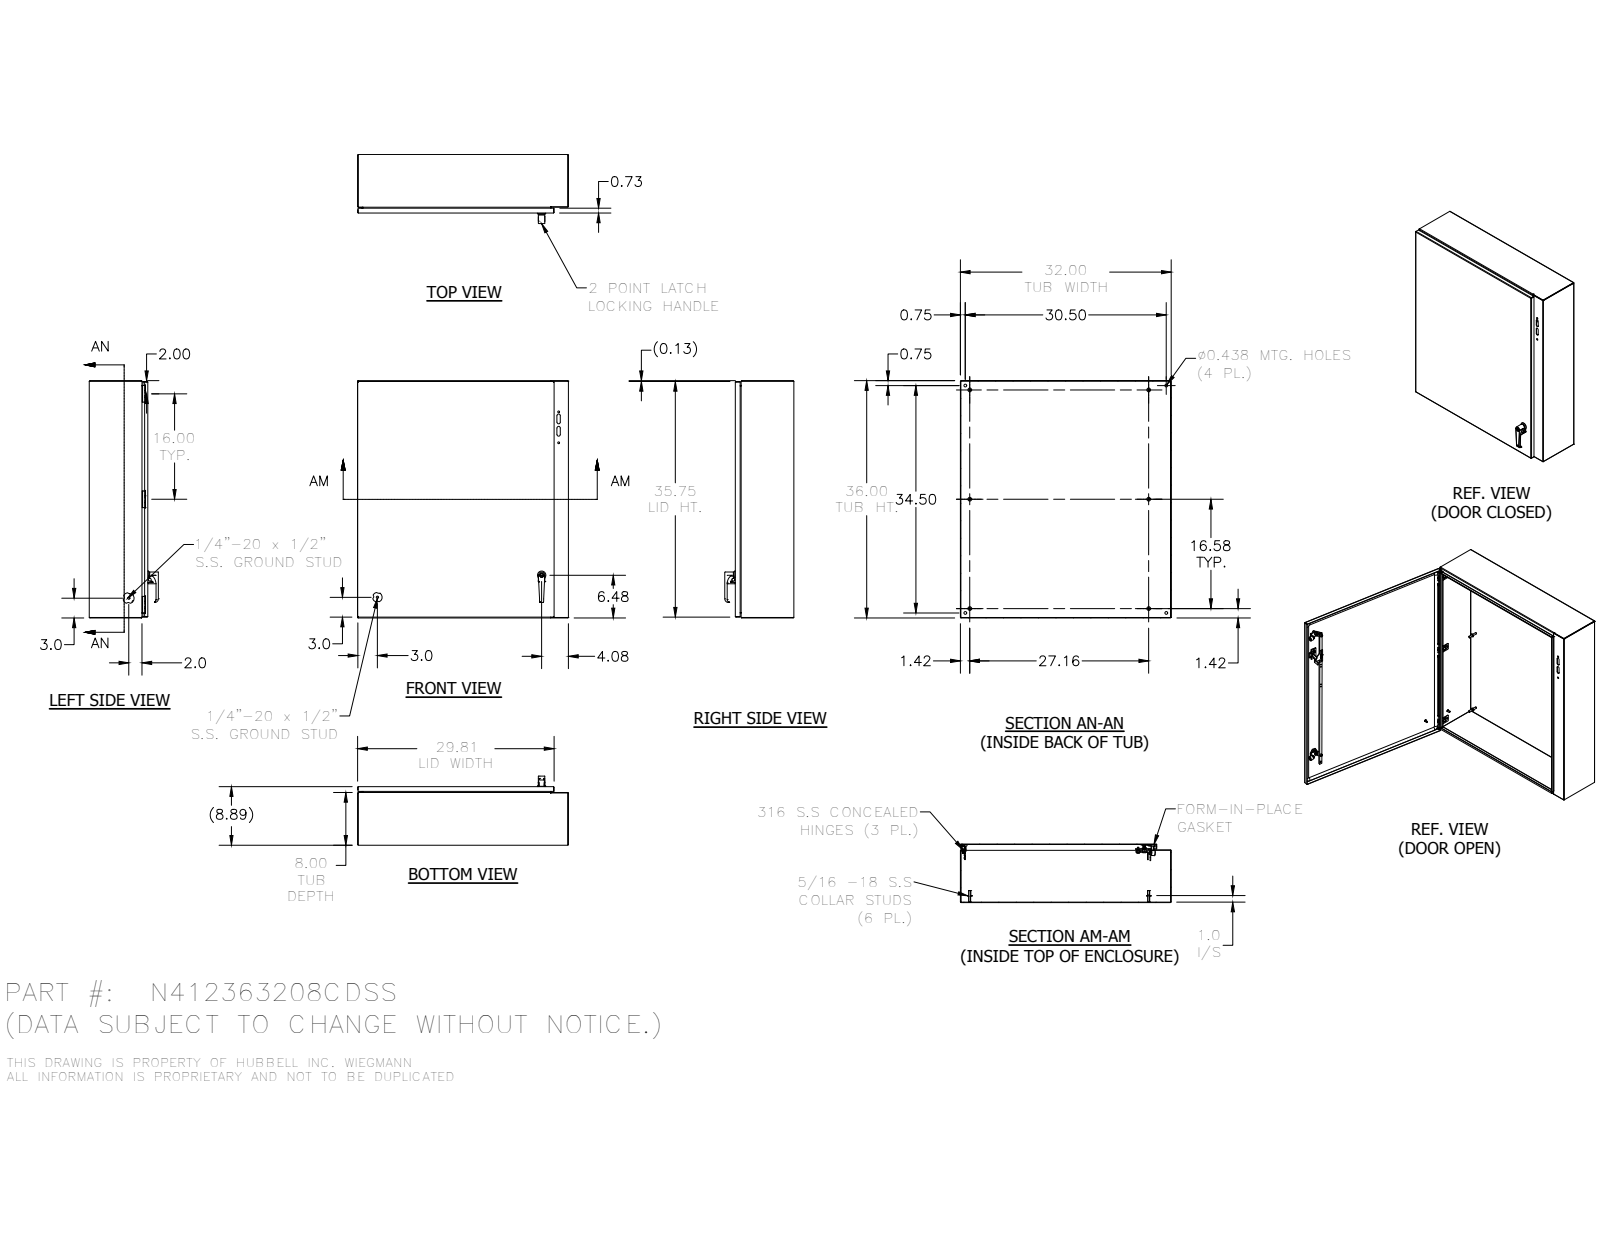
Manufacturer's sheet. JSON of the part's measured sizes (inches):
{"part_name": "N412363208CD", "step_written_by": "SolidWorks 2019 (AUTOMOTIVE_DESIGN)", "units": "inches", "bodies": {"solids": 71, "faces": 2508, "planar": 937, "cylindrical": 920, "other": 651}, "overall_size": [36, 32, 10.512], "volume_in3": 277.6, "surface_area_in2": 7446, "round_holes": [[0.093, 6], [0.145, 6], [0.152, 6], [0.167, 6], [0.172, 6], [0.187, 6], [0.156, 5], [0.437, 4], [0.32, 3], [0.196, 2], [0.211, 2], [0.22, 2]], "round_bosses_or_shafts": [[0.25, 16], [0.3, 10], [0.563, 6], [0.36, 6], [0.32, 6], [0.275, 6], [0.256, 6], [0.164, 6]], "partial_cylinders_radius": [[0.02, 38], [0.05, 38], [0.125, 33], [0.012, 30], [0.016, 26], [0.031, 18], [0.016, 16], [0.025, 16]], "face_to_face_distances": [0.074, 8.843, 8.769, 8.917, 31.926, 35.926, 0.917, 7.926, 32, 31.852], "hole_center_spacings": [16, 0.5, 32, 16.008, 0.66, 1.307, 1.965, 26.9]}
